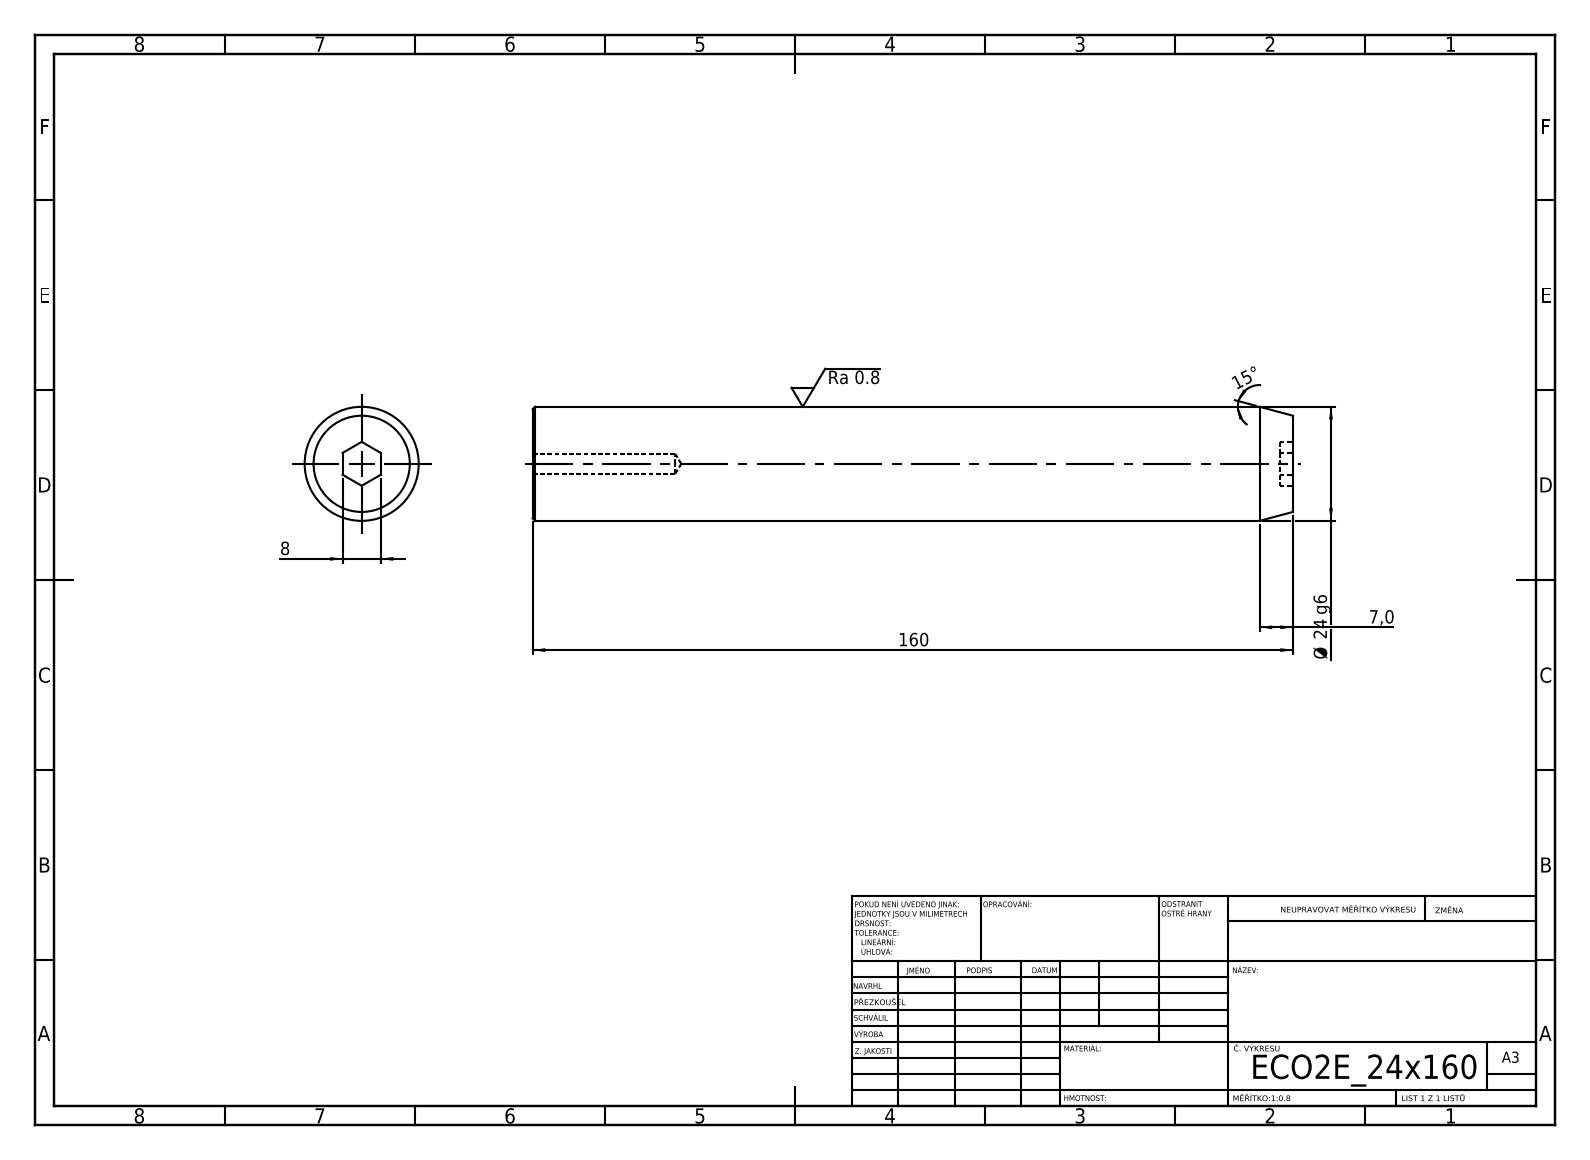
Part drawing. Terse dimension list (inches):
written by: SolidWorks 2019 (CONFIG_CONTROL_DESIGN)
unit: in
bodies: 1 solid, 19 faces (9 planar, 4 cylindrical, 6 other)
size: 6.299 × 0.945 × 0.945
volume: 4.353 in³; area: 20.56 in²
holes: 1× ⌀0.165
bosses: 1× ⌀0.945
face distances: 6.299, 0.11, 6.189, 0.315
